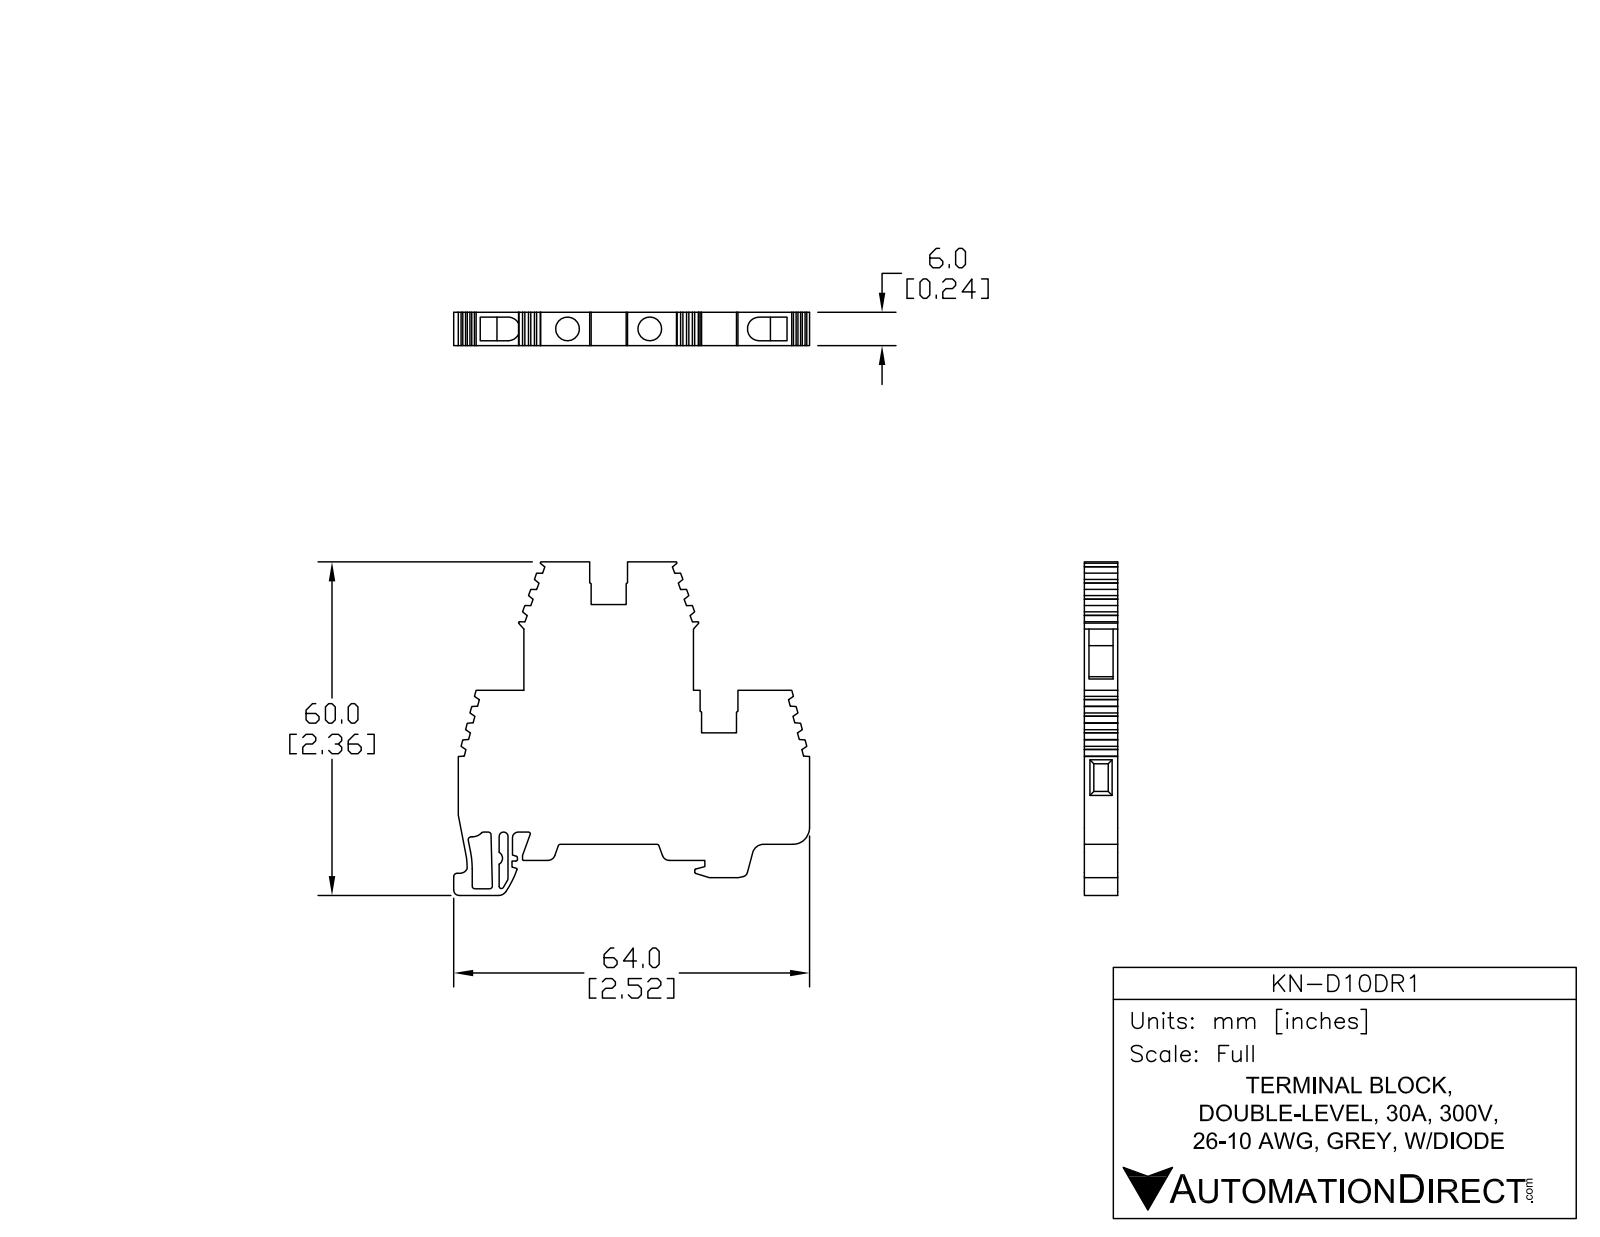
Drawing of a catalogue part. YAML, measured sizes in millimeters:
part_name: "KN-D10DR1"
step_written_by: "SolidWorks 2014 (AUTOMOTIVE_DESIGN)"
units: millimeters
bodies: {solids: 1, faces: 235, planar: 192, cylindrical: 43, other: 0}
overall_size: [64.03, 60, 6]
volume: 13659
surface_area: 7432
round_holes:
  - {diameter: 4.25, count: 2}
partial_cylinders:
  - {radius: 0.5, count: 7}
  - {radius: 0.3, count: 6}
  - {radius: 0.2, count: 3}
  - {radius: 1, count: 3}
  - {radius: 0.6, count: 2}
  - {radius: 2.12, count: 2}
  - {radius: 0.4, count: 1}
  - {radius: 0.8, count: 1}
face_to_face_distances: [6, 2.93, 0.83, 5.17, 23.08, 6.55, 19.86, 6.3, 4, 5.86]
hole_center_spacings: [14.8]
